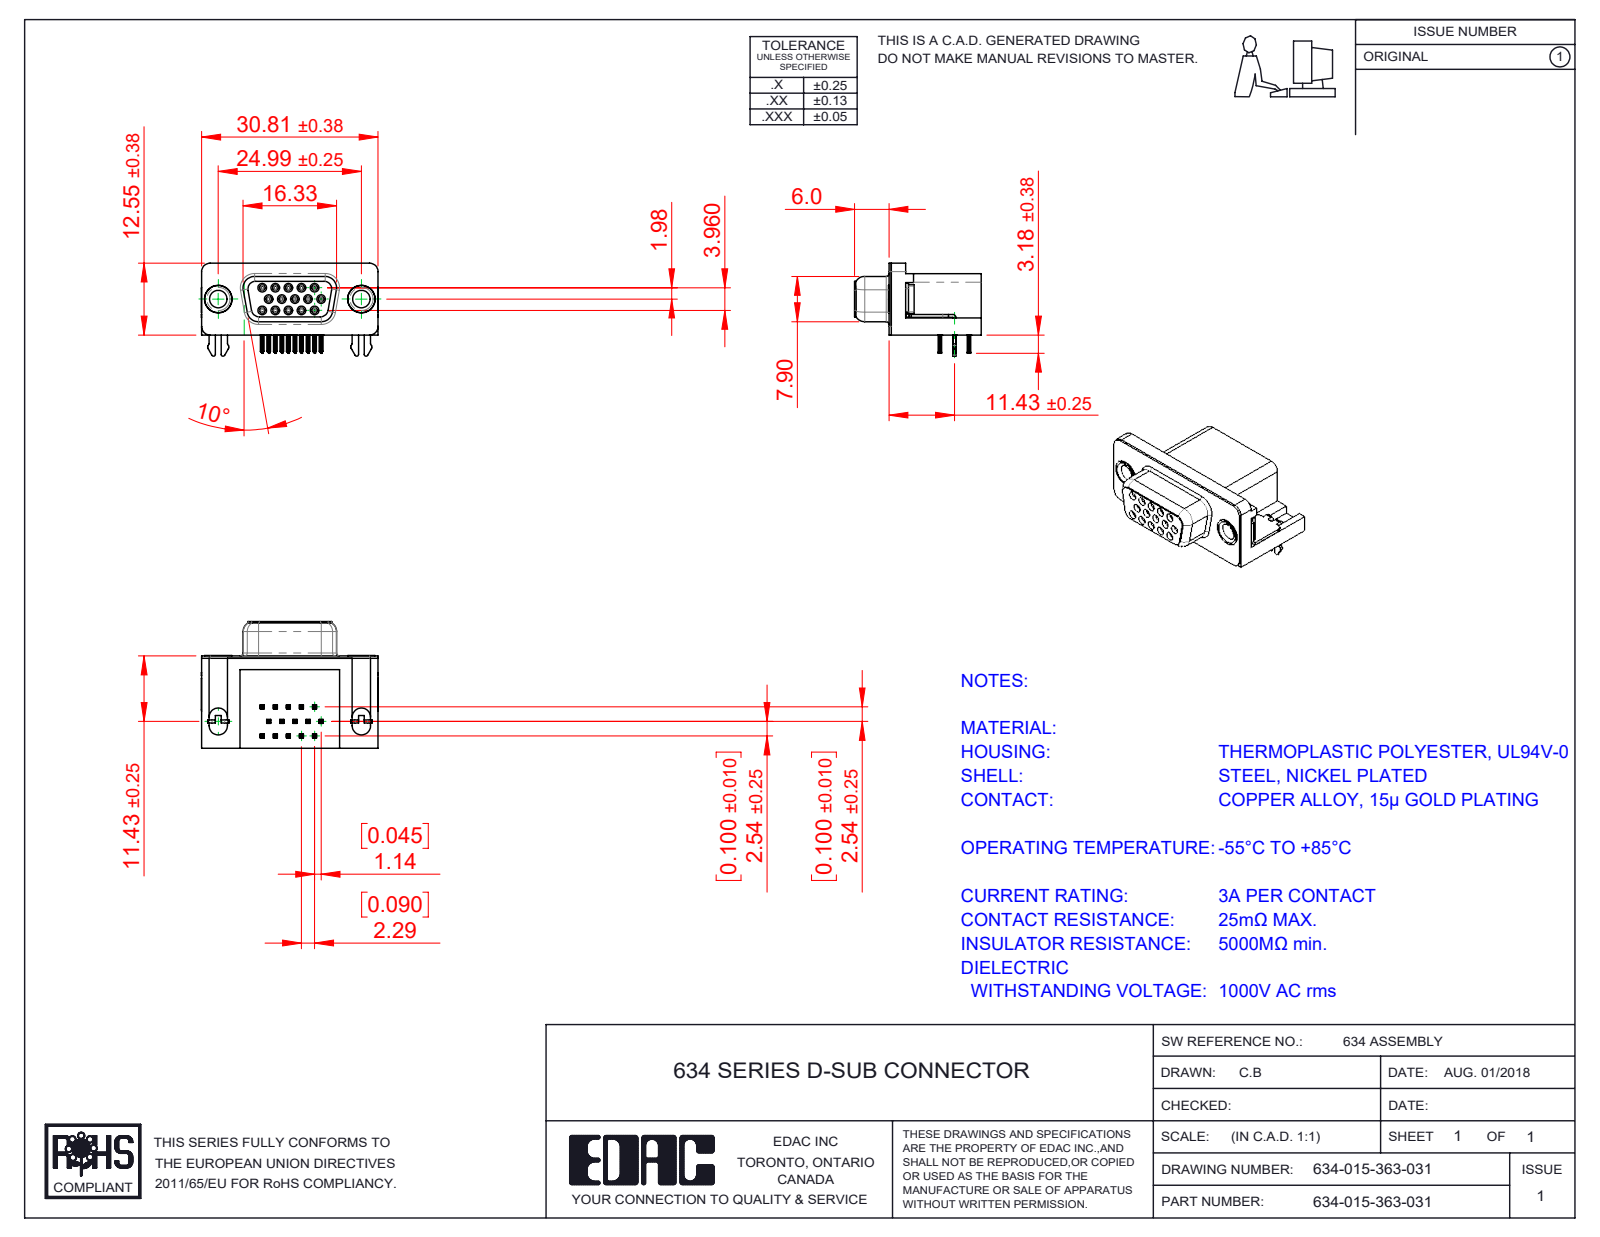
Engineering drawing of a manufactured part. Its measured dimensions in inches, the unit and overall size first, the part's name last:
Units: inches
Overall size (bounding box): 1.216 × 0.87 × 0.64
Round holes (diameter × count): ⌀0.031 ×15, ⌀0.035 ×15, ⌀0.12 ×2, ⌀0.157 ×2, ⌀0.189 ×2, ⌀0.197 ×2
Round bosses / shafts (diameter × count): ⌀0.047 ×15, ⌀0.193 ×2, ⌀0.187 ×2, ⌀0.152 ×2
Partial cylindrical surfaces — rounded edges, fillets, slot ends (radius × count): R0.004 ×120, R0.006 ×60, R0.014 ×30, R0.039 ×19, R0.013 ×15, R0.02 ×10, R0.01 ×8, R0.053 ×8
Main face-to-face distances: 0.016, 0.407, 0.618, 0.634, 0.014, 0.098, 0.114, 0.252, 0.02, 0.024
Hole centre spacings: 0.09, 0.09, 0.156, 0.18, 0.238, 0.156, 0.18, 0.27
Volume: 0.277 in³ · Surface area: 10.05 in²
Bodies: 21 solids, 2421 faces (1098 planar, 589 cylindrical, 734 other)
Part name (STEP PRODUCT): Contact Bottom; 634 Shell; Contact Middle; 634 Housing (+4 more)
STEP written by: SolidWorks 2016 (CONFIG_CONTROL_DESIGN)
